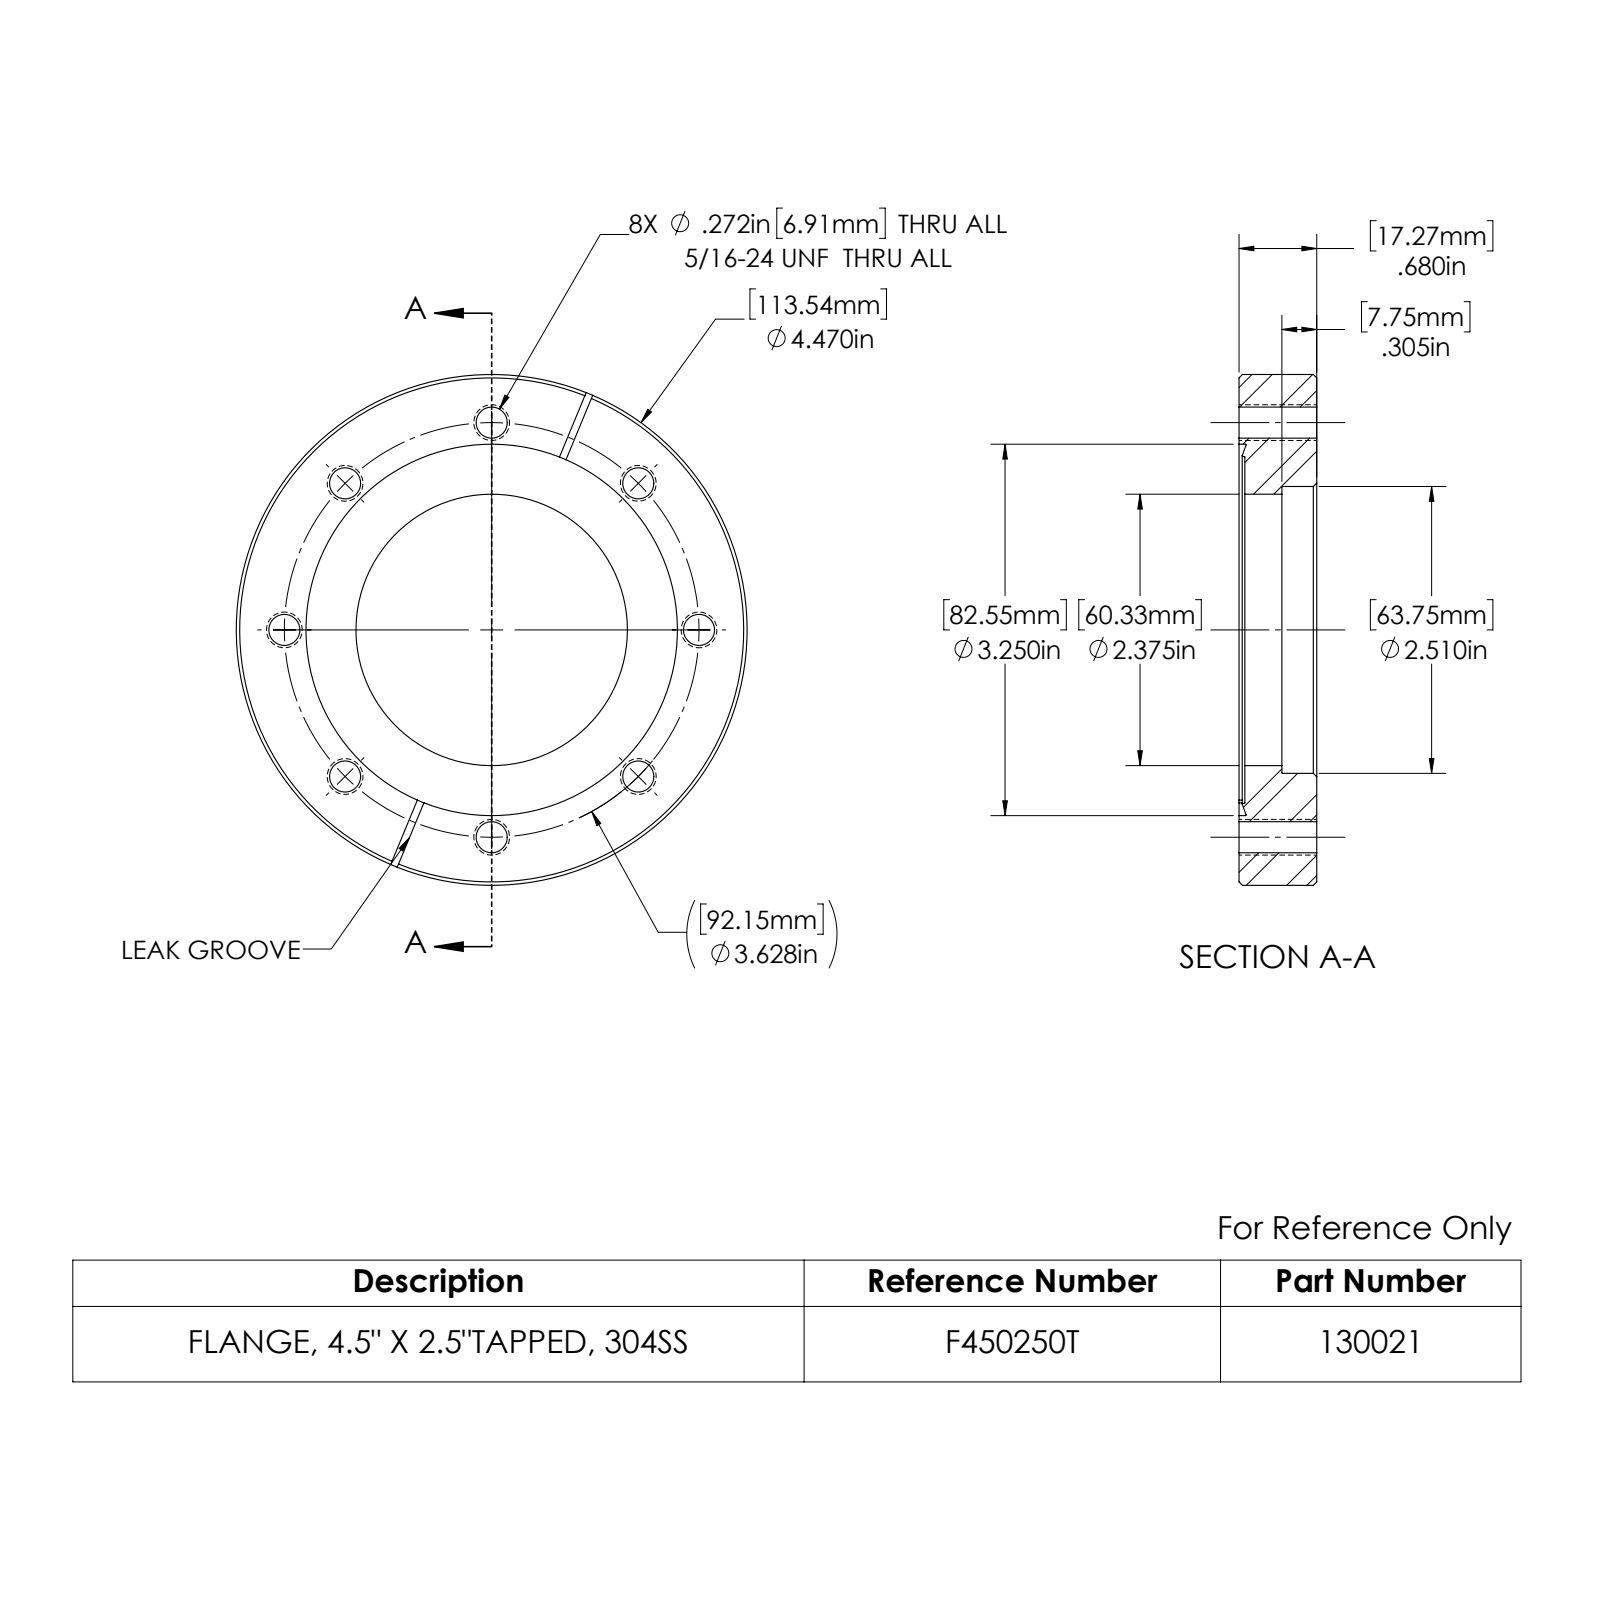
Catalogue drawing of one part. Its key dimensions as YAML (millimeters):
part_name: "130021"
step_written_by: "SolidWorks 2022 (AUTOMOTIVE_DESIGN)"
units: millimeters
bodies: {solids: 1, faces: 54, planar: 11, cylindrical: 24, other: 19}
overall_size: [113.5, 113.5, 17.3]
volume: 114300
surface_area: 26390
round_holes:
  - {diameter: 6.9, count: 8}
  - {diameter: 60.3, count: 1}
  - {diameter: 63.8, count: 1}
  - {diameter: 82.6, count: 1}
round_bosses_or_shafts:
  - {diameter: 113.5, count: 1}
face_to_face_distances: [17.3, 1.3, 16, 9.5, 8.2, 7.7, 1.3, 8.2, 16, 1.6]
hole_center_spacings: [35.3, 46.1, 85.1, 65.2, 65.2, 92.2, 92.2]
